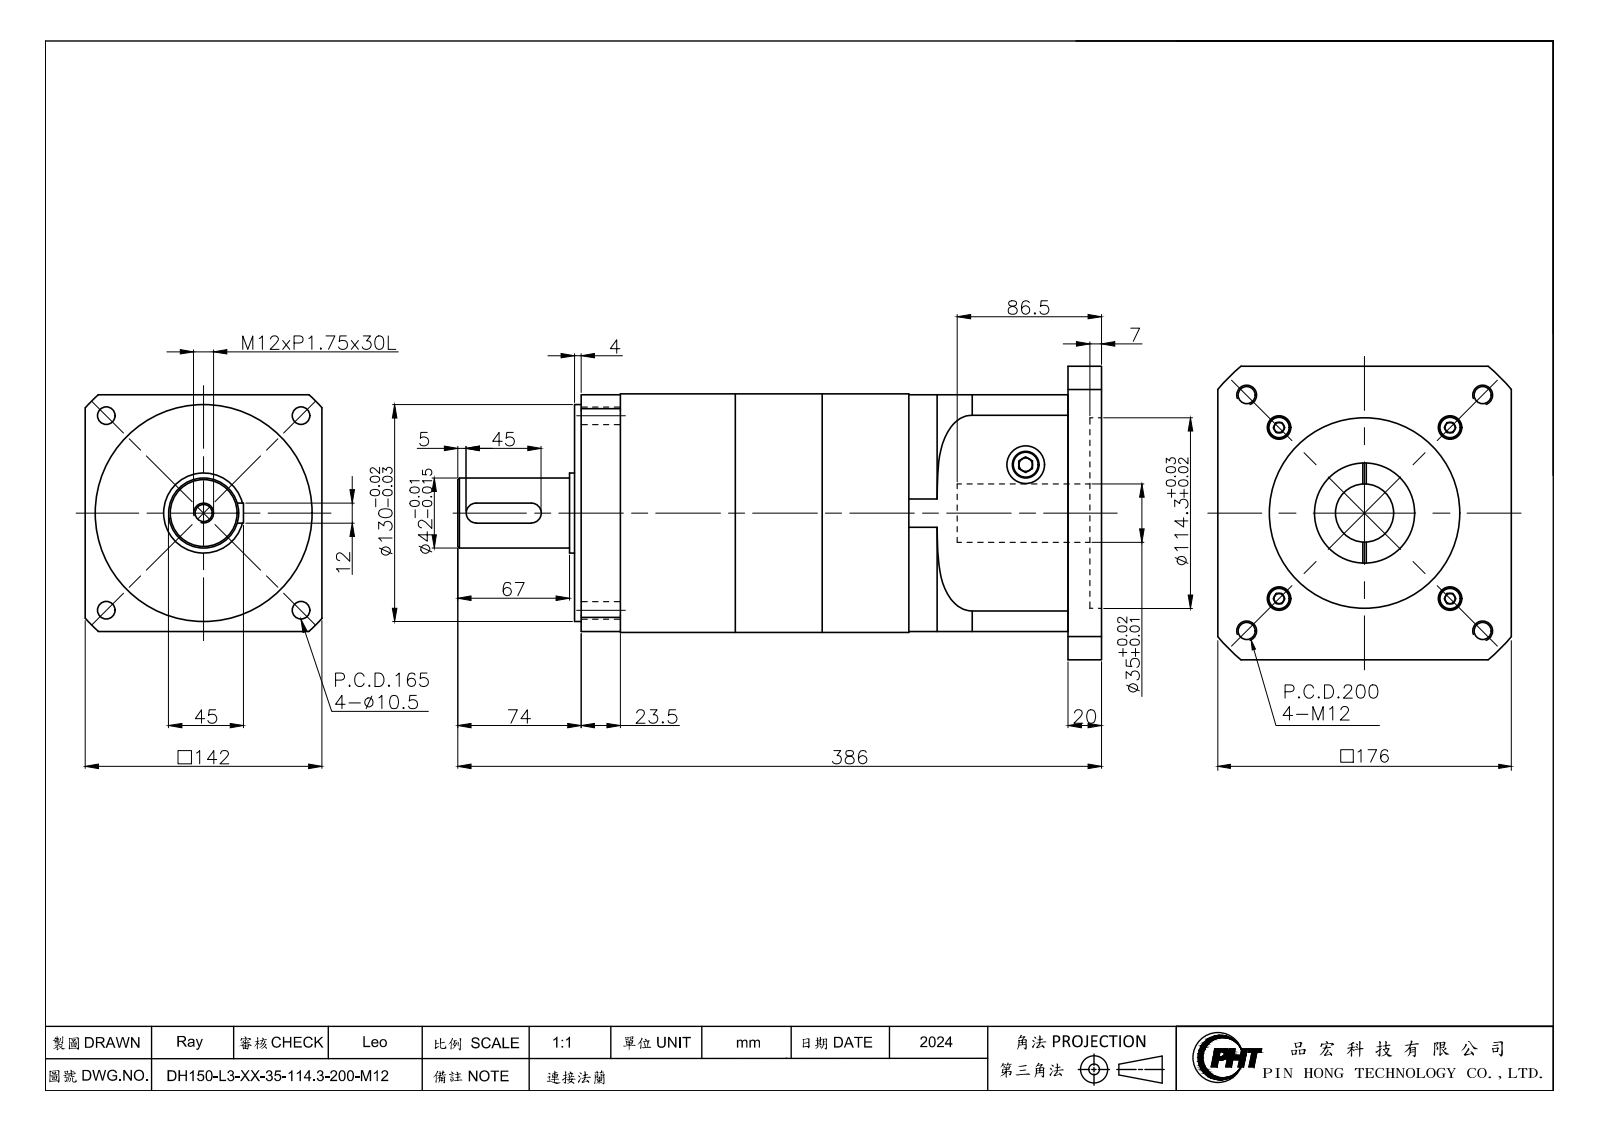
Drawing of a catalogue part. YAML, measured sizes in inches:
part_name: "DH150-L3-XX-35-114.3-200-M12(連接法蘭)_2024"
step_written_by: "SolidWorks 2016 (CONFIG_CONTROL_DESIGN)"
units: inches
bodies: {solids: 21, faces: 400, planar: 175, cylindrical: 161, other: 64}
overall_size: [15.197, 6.929, 6.929]
volume: 330.1
surface_area: 778.8
round_holes:
  - {diameter: 0.551, count: 8}
  - {diameter: 0.402, count: 5}
  - {diameter: 0.268, count: 4}
  - {diameter: 0.354, count: 4}
  - {diameter: 0.413, count: 4}
  - {diameter: 0.591, count: 4}
  - {diameter: 0.886, count: 2}
  - {diameter: 1.378, count: 1}
  - {diameter: 2.362, count: 1}
  - {diameter: 3.622, count: 1}
  - {diameter: 4.331, count: 1}
  - {diameter: 4.5, count: 1}
round_bosses_or_shafts:
  - {diameter: 0.48, count: 12}
  - {diameter: 0.315, count: 12}
  - {diameter: 5.669, count: 1}
  - {diameter: 5.63, count: 1}
  - {diameter: 5.118, count: 1}
  - {diameter: 2.913, count: 1}
  - {diameter: 1.89, count: 1}
  - {diameter: 1.654, count: 1}
partial_cylinders:
  - {radius: 0.236, count: 2}
  - {radius: 3.642, count: 1}
  - {radius: 3.74, count: 1}
  - {radius: 4.528, count: 1}
face_to_face_distances: [2.047, 4.094, 6.811, 4.764, 2.717, 3.76, 5.807, 7.854, 10.571, 5.63]
hole_center_spacings: [2.598, 0.756, 0.999, 1.578, 3.326, 3.596, 3.675, 4.118]
